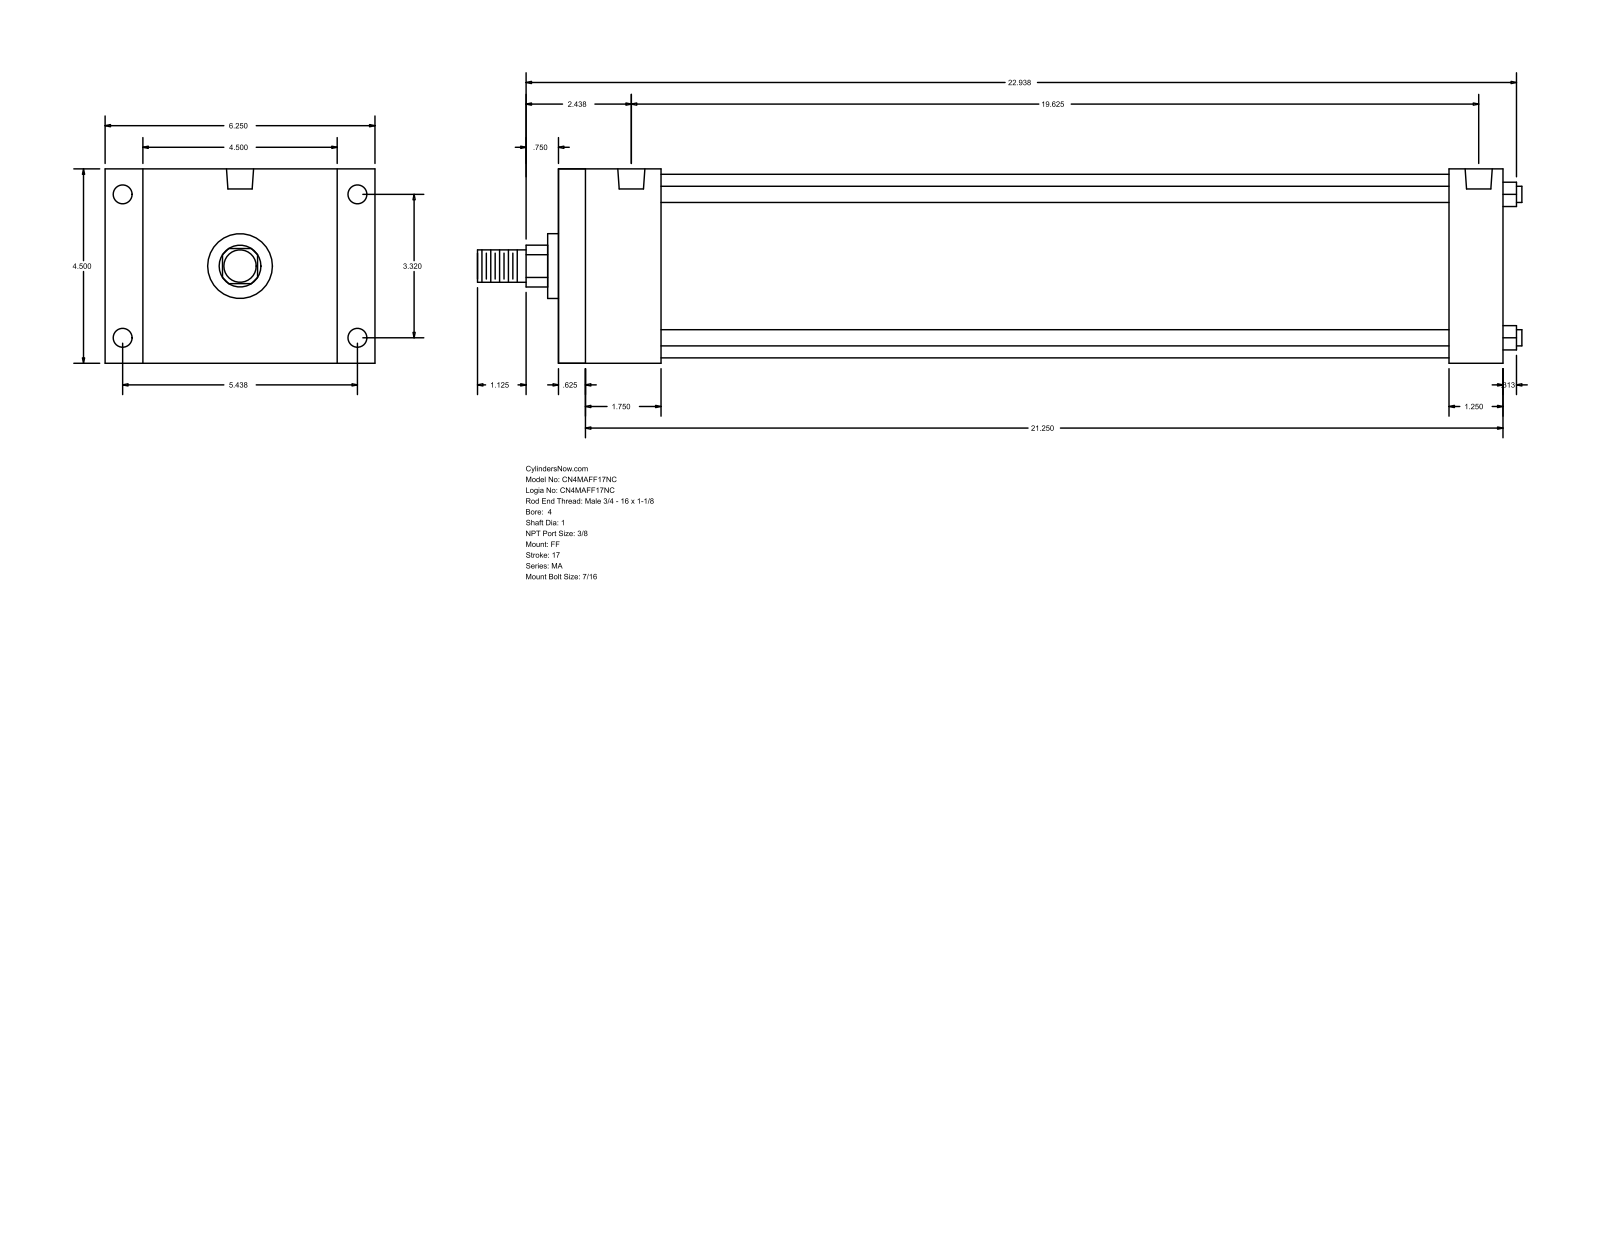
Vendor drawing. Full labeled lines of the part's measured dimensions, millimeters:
Part name (STEP PRODUCT): MA_FF__0400_1
STEP written by: GSSL Pune (CONFIG_CONTROL_DESIGN)
Units: millimetres
Bodies: 0 solids, 92 faces (64 planar, 28 cylindrical, 0 other)
Overall size (bounding box): 614.36 × 158.75 × 114.3
Round holes (diameter × count): ⌀11.11 ×8, ⌀15.93 ×2
Round bosses / shafts (diameter × count): ⌀9.53 ×4, ⌀107.95 ×1, ⌀38.1 ×1, ⌀25.4 ×1, ⌀19.05 ×1
Partial cylindrical surfaces — rounded edges, fillets, slot ends (radius × count): R12.29 ×1
Main face-to-face distances: 114.3, 555.62, 15.87, 539.75, 22.23, 136.53, 523.87, 508, 31.75, 60.33
Hole centre spacings: 84.32, 138.12, 161.82, 488.95, 4.76, 4.77, 493.71, 493.72
